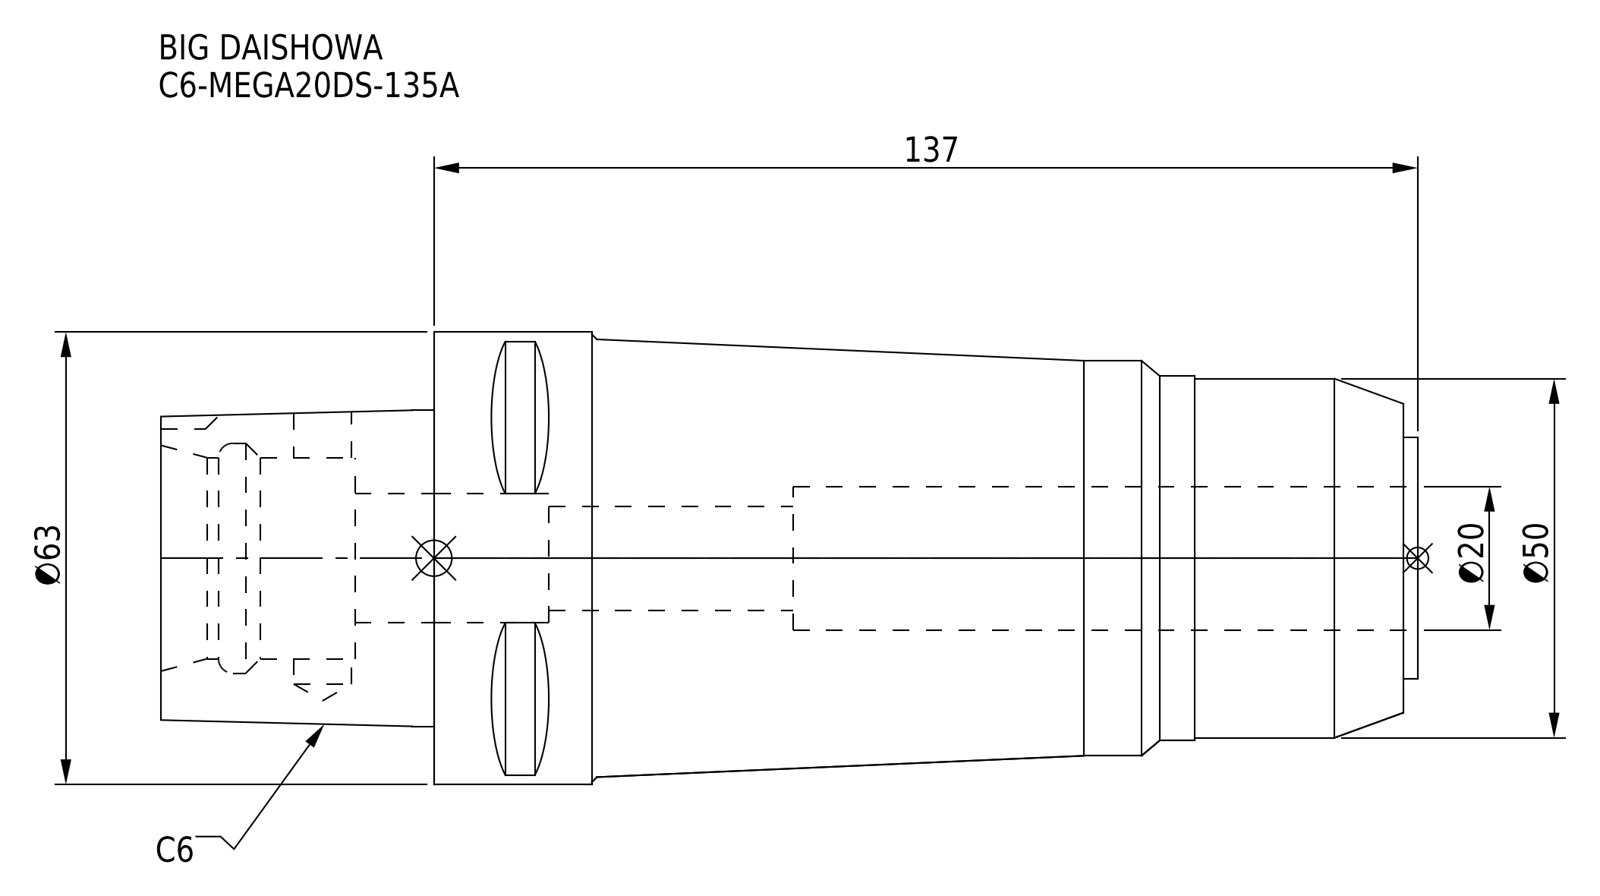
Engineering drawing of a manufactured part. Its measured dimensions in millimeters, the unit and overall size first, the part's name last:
Units: millimetres
Overall size (bounding box): 175 × 63 × 63
Round holes (diameter × count): ⌀8.1 ×1, ⌀14.5 ×1, ⌀18 ×1, ⌀20 ×1, ⌀28 ×1, ⌀32 ×1
Round bosses / shafts (diameter × count): ⌀63 ×1, ⌀55 ×1, ⌀50.7 ×1, ⌀50 ×1, ⌀33.6 ×1
Partial cylindrical surfaces — rounded edges, fillets, slot ends (radius × count): R5 ×1
Main face-to-face distances: 137, 2, 135, 175, 173, 38, 27, 148, 146, 11
Volume: 335 637 mm³ · Surface area: 45 317 mm²
Bodies: 1 solid, 76 faces (31 planar, 27 cylindrical, 18 other)
Part name (STEP PRODUCT): C6-MEGA20DS-135A
STEP written by: CREO PARAMETRIC BY PTC INC, 2016380 (AUTOMOTIVE_DESIGN)
